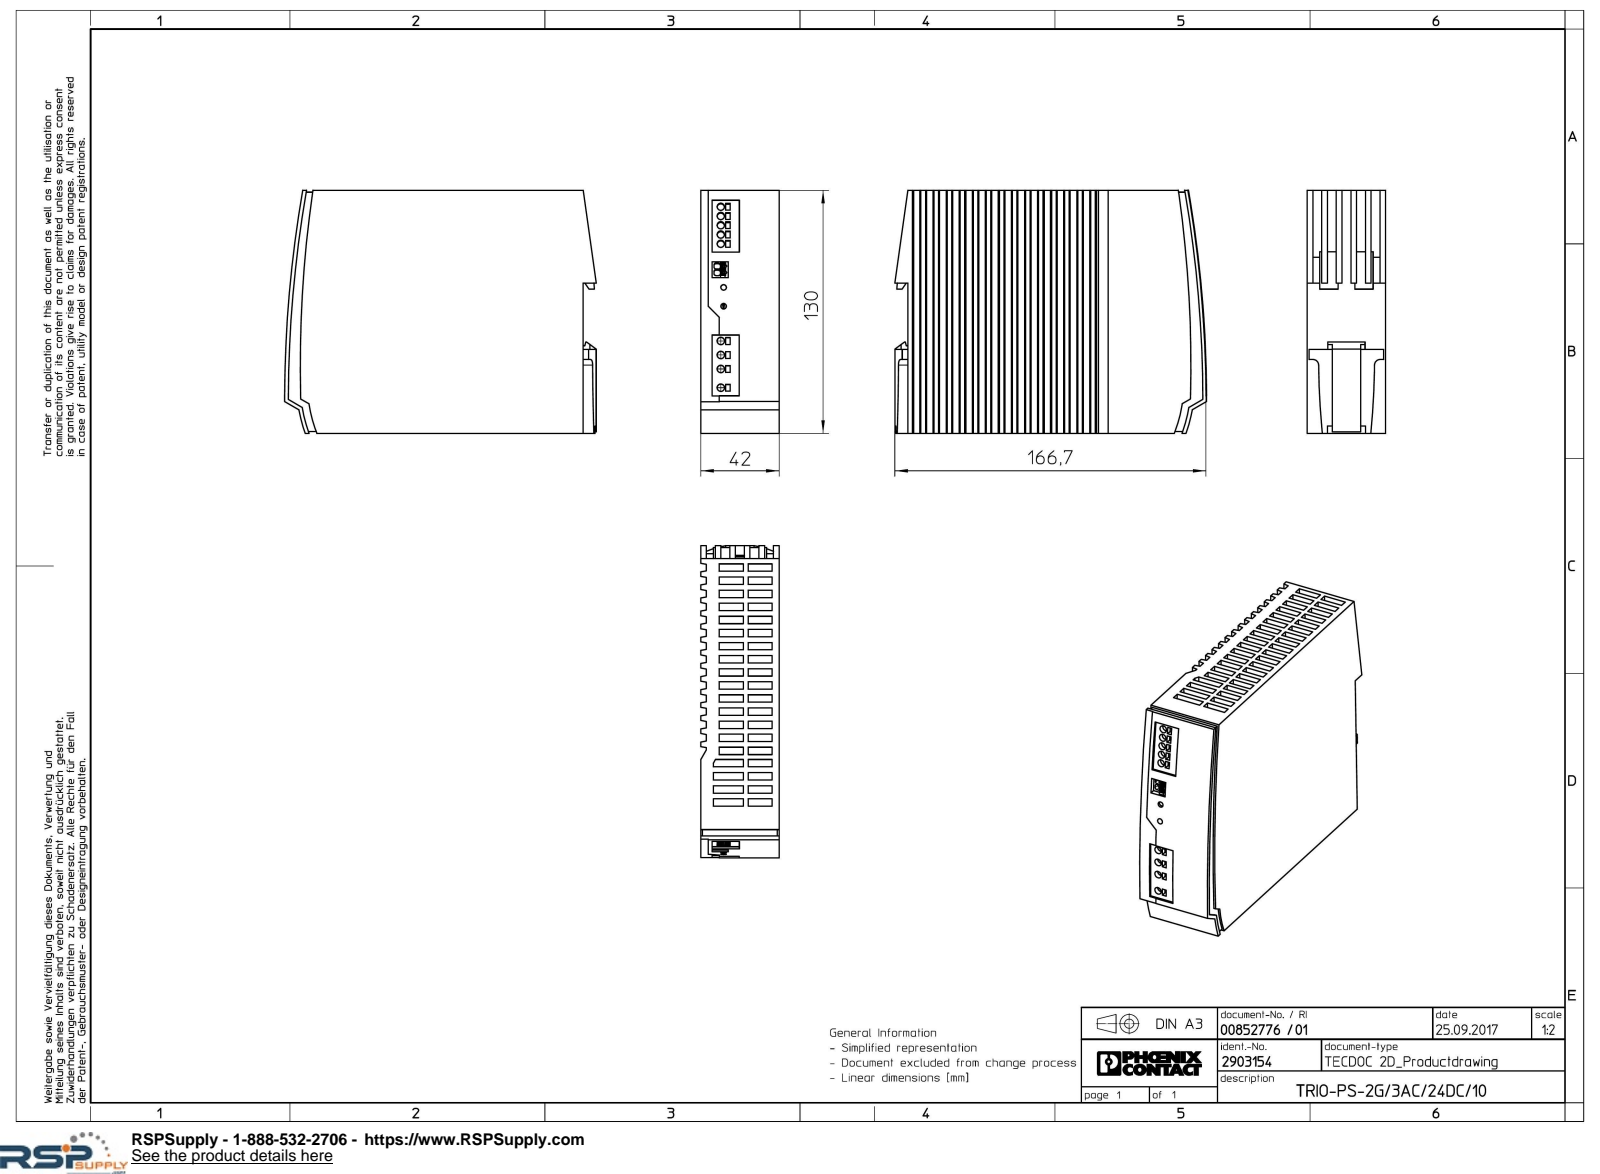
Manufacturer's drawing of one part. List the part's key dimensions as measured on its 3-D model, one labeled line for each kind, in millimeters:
Part name (STEP PRODUCT): TRIO_PS_2G_3AC_24DC_10-select
STEP written by: Creo Elements/Direct Modeling 20.1A 29-Sep-2018 (C) Parametric Technology GmbH (AUTOMOTIVE_DESIGN)
Units: millimetres
Bodies: 1 solid, 707 faces (656 planar, 47 cylindrical, 4 other)
Overall size (bounding box): 167 × 130 × 42
Volume: 826 537 mm³ · Surface area: 86 421 mm²
Round holes (diameter × count): ⌀4 ×9, ⌀3 ×2
Partial cylindrical surfaces — rounded edges, fillets, slot ends (radius × count): R0.57 ×2, R0.6 ×2, R1.03 ×2, R1.04 ×2, R3 ×2, R430 ×2, R40 ×1, R46.1 ×1
Main face-to-face distances: 3, 42, 13.79, 27.58, 39, 41.37, 6.89, 6.9, 55.16, 20.68
Hole centre spacings: 5, 10, 15, 7.49, 7.5, 14.99, 17.5, 19.99
